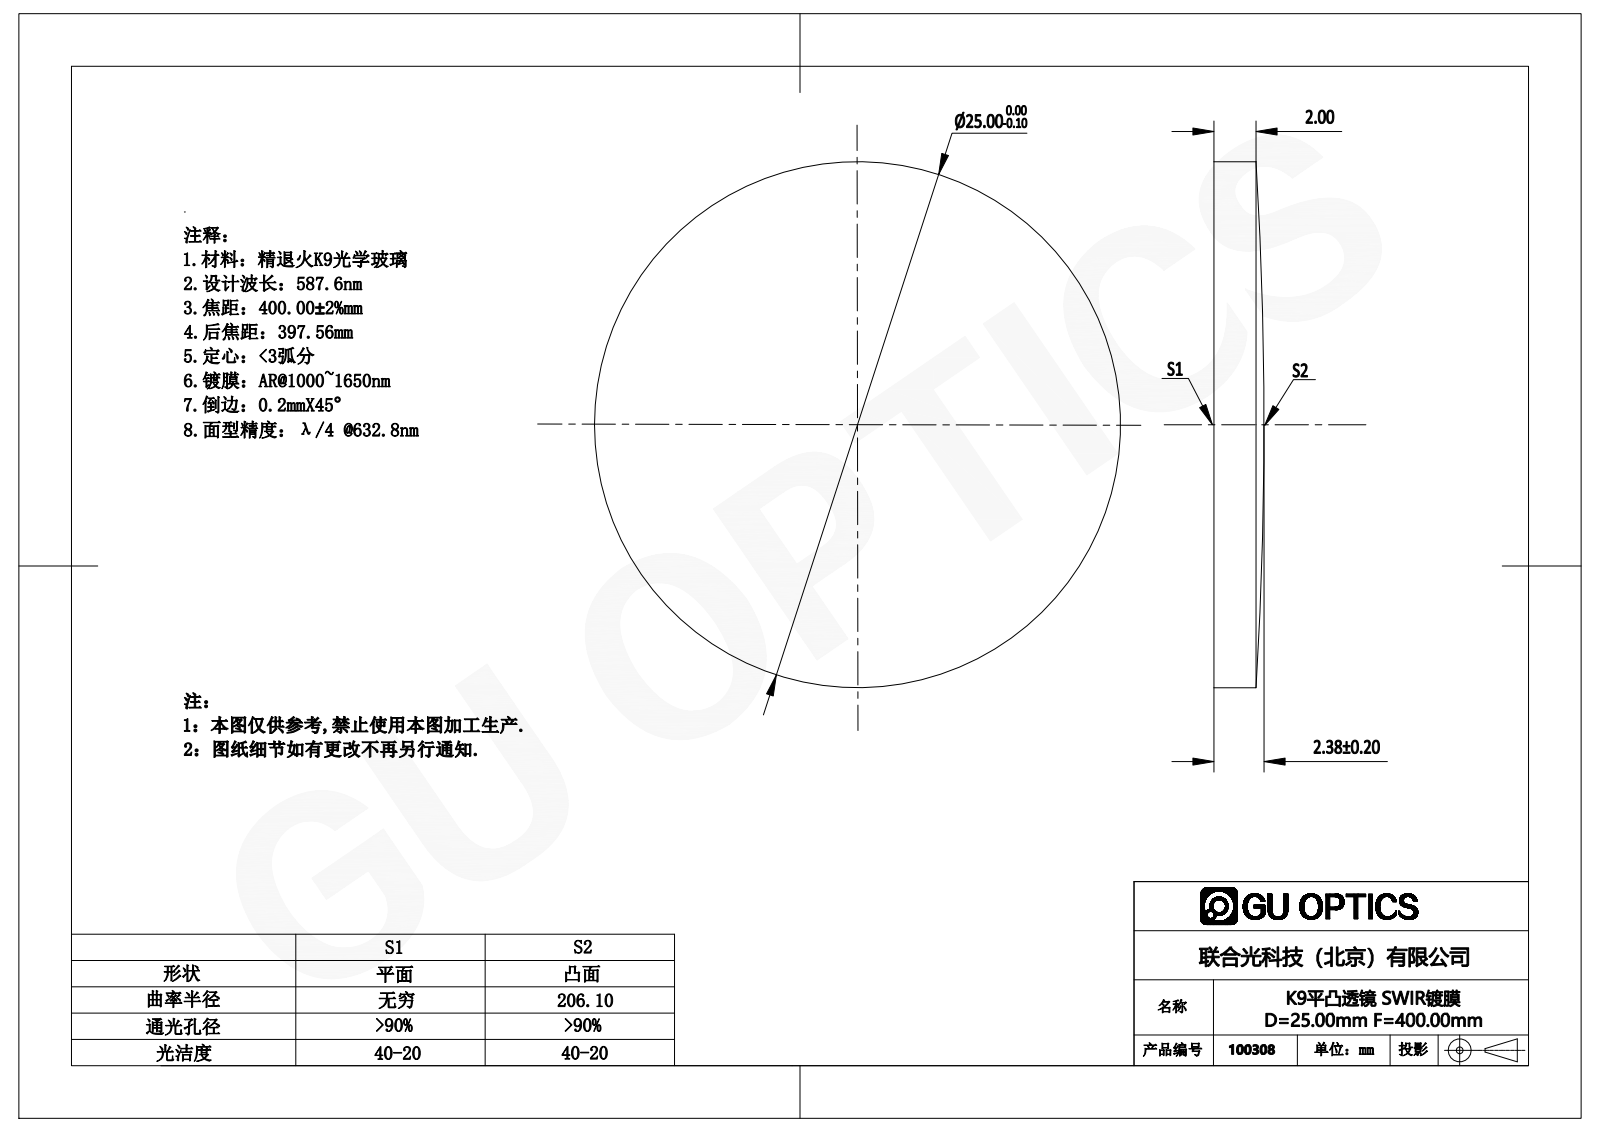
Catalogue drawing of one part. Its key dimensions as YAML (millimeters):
part_name: "100136"
step_written_by: "SolidWorks 2016 (AUTOMOTIVE_DESIGN)"
units: millimeters
bodies: {solids: 1, faces: 5, planar: 1, cylindrical: 2, other: 2}
overall_size: [25, 25, 2.38]
volume: 1075
surface_area: 1139
round_bosses_or_shafts:
  - {diameter: 25, count: 1}
